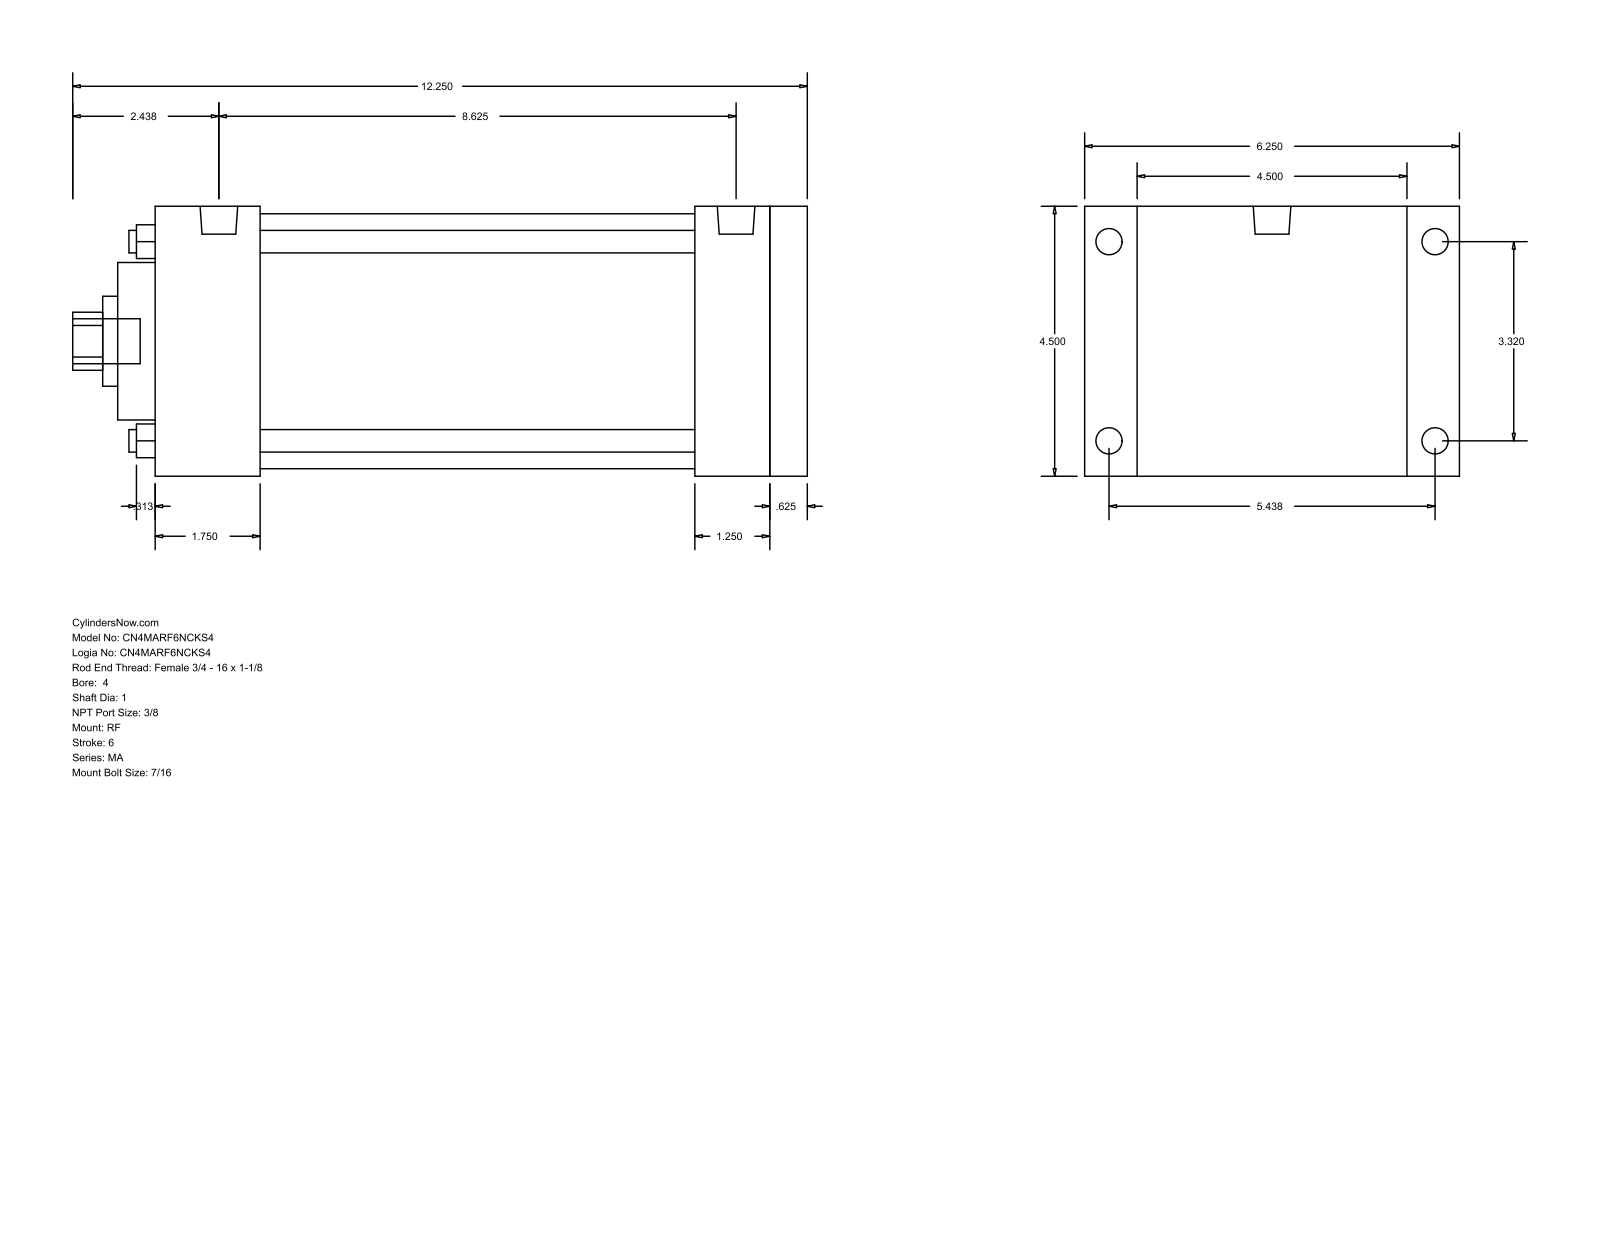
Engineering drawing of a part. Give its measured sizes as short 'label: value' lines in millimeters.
name: MA_RF__0400_1
written by: GSSL Pune (CONFIG_CONTROL_DESIGN)
unit: mm
bodies: 0 solids, 94 faces (65 planar, 29 cylindrical, 0 other)
size: 311.15 × 158.75 × 114.3
holes: 4× ⌀9.53, 1× ⌀25.4, 1× ⌀38.1, 1× ⌀66.67, 1× ⌀107.95
bosses: 8× ⌀11.11, 2× ⌀15.93, 1× ⌀19.05
rounds: 1× R12.29
face distances: 114.3, 276.23, 260.35, 15.88, 22.23, 136.53, 228.6, 31.75, 47.63, 44.46
hole spacings: 59.62, 84.32, 119.25
